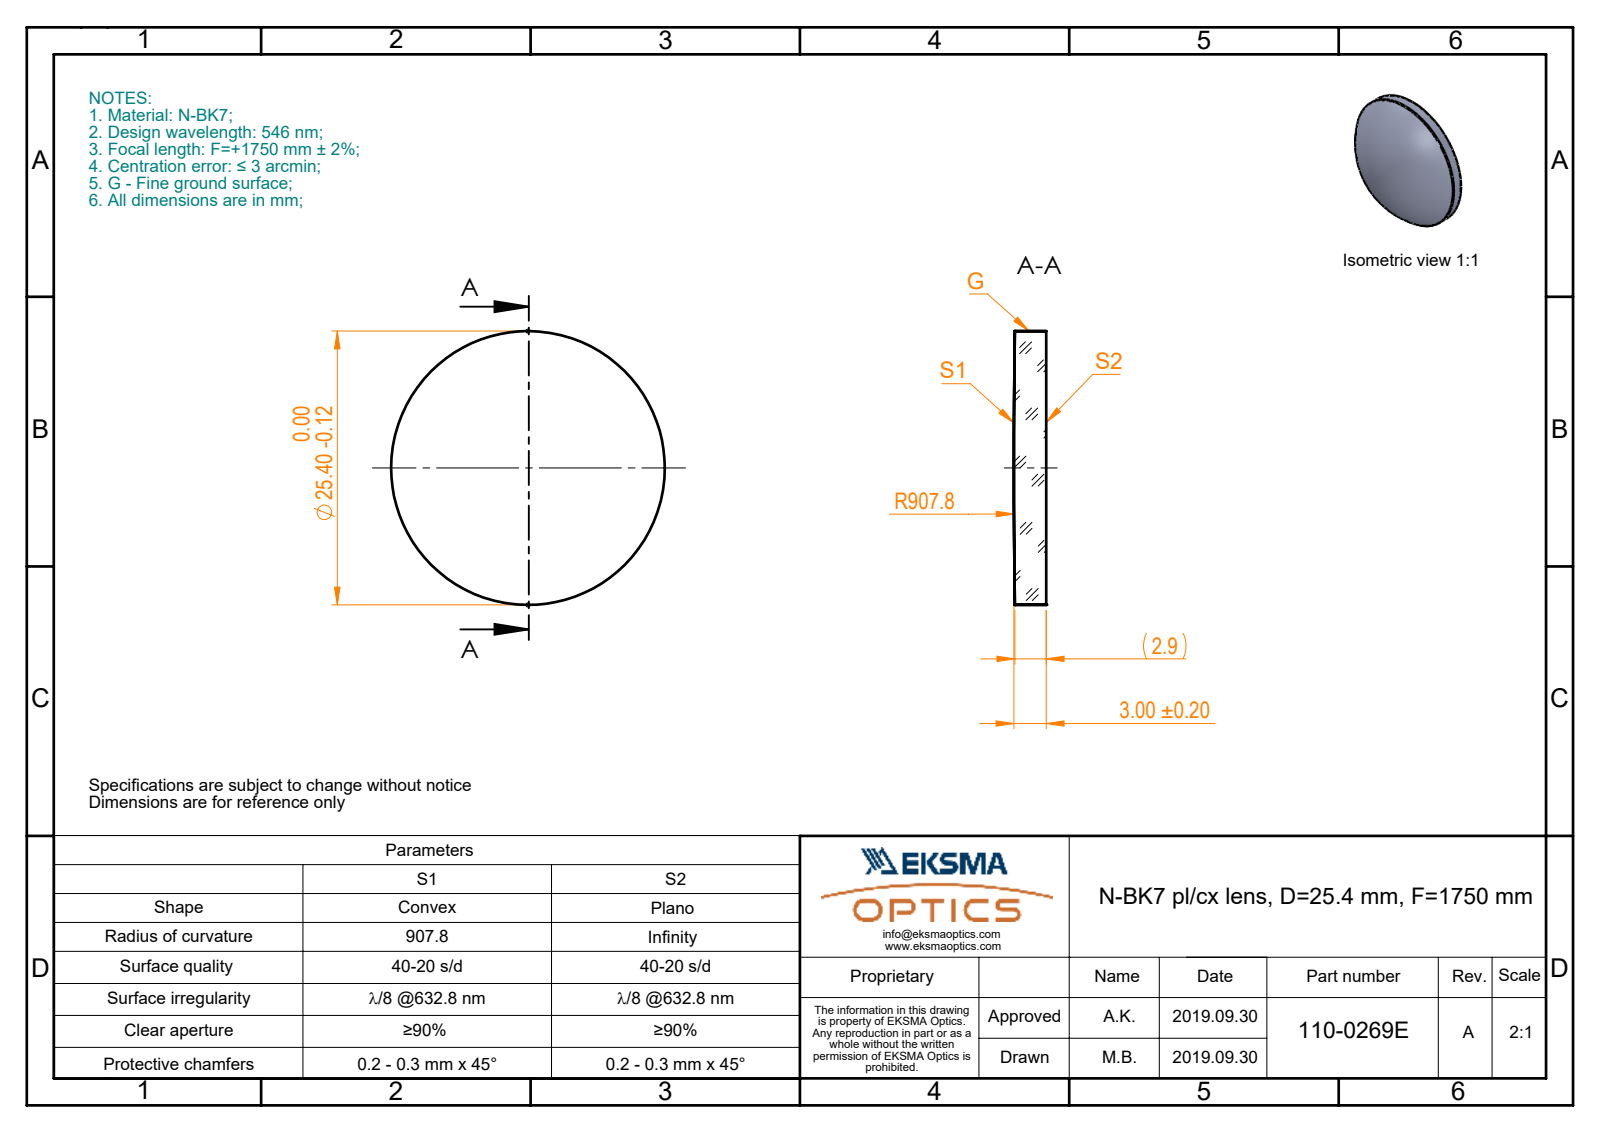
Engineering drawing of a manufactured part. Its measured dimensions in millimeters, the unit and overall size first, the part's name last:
Units: millimetres
Overall size (bounding box): 25.4 × 25.4 × 3
Round bosses / shafts (diameter × count): ⌀25.4 ×1
Volume: 1 498 mm³ · Surface area: 1 246 mm²
Bodies: 1 solid, 4 faces (1 planar, 2 cylindrical, 1 other)
Part name (STEP PRODUCT): 110-0269E BK7 pl-cx 25.4 F1750
STEP written by: SolidWorks 2019 (CONFIG_CONTROL_DESIGN)
